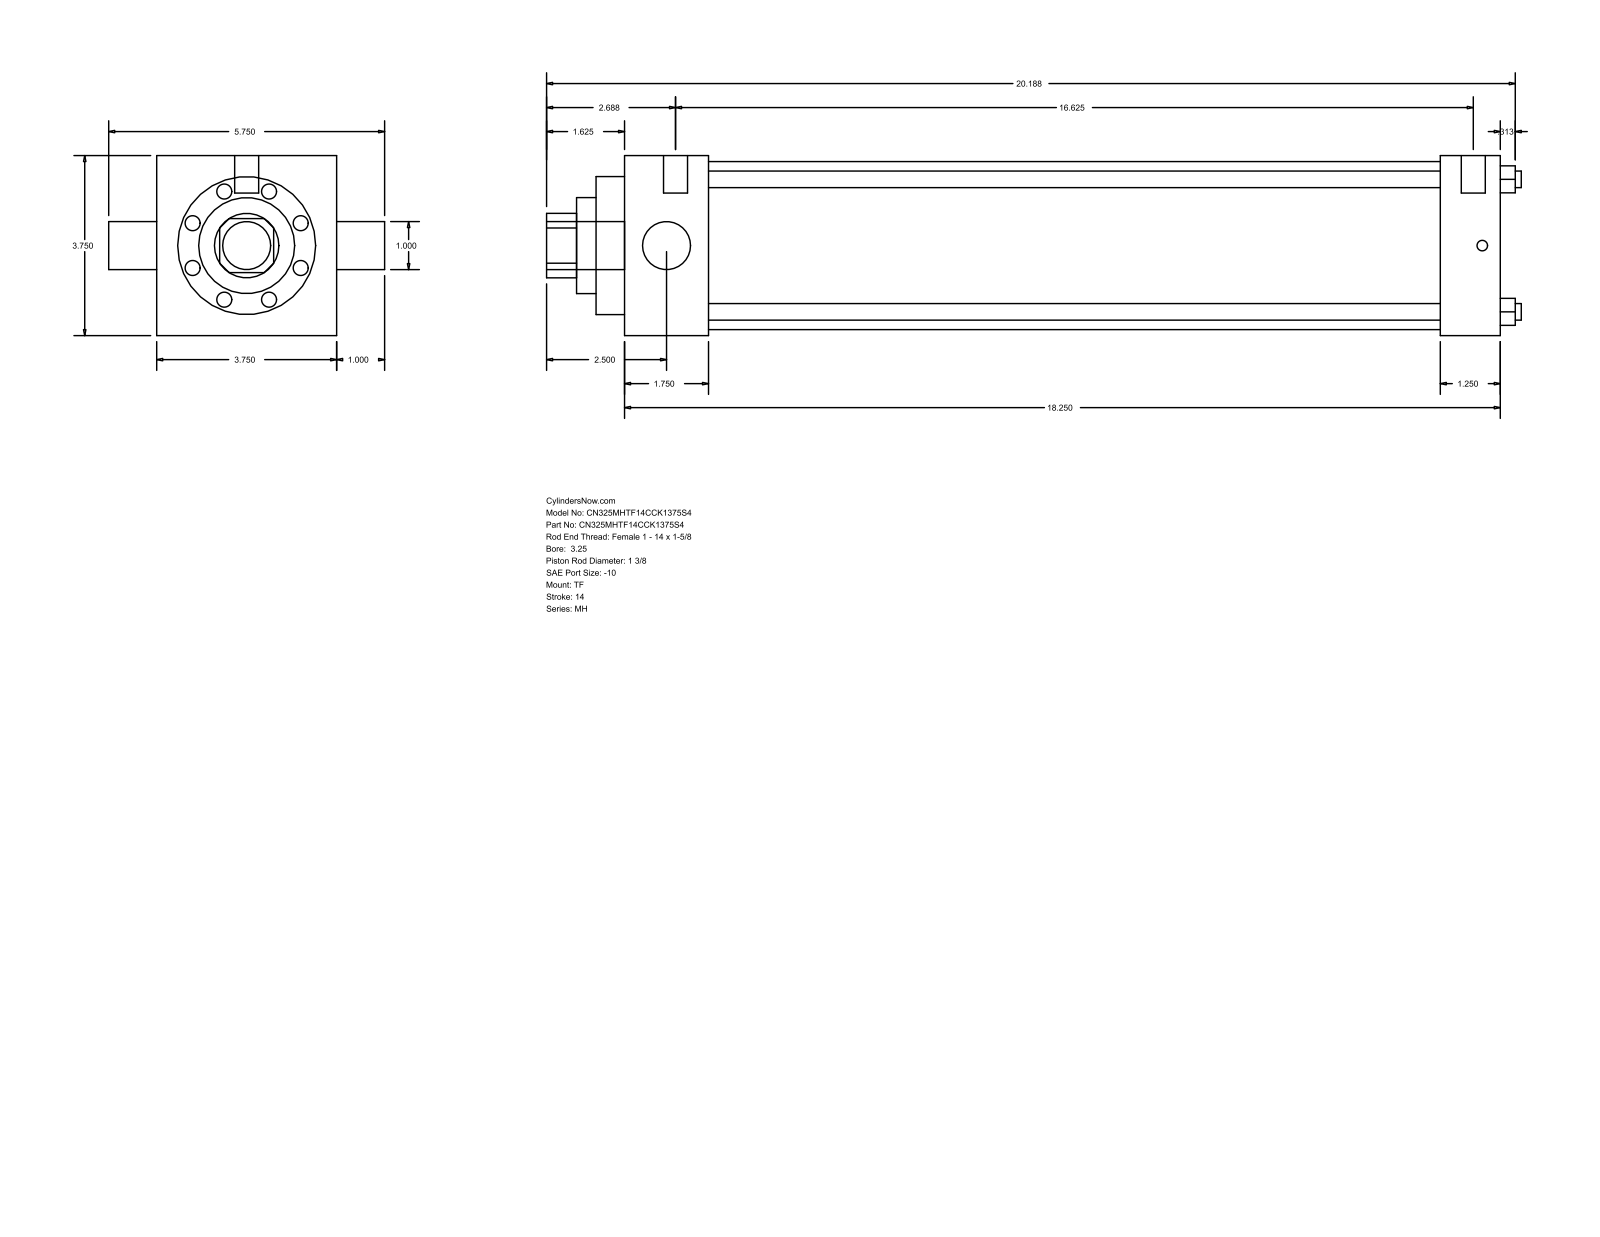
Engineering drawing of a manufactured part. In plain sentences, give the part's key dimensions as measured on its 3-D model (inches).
The part is named "MH_TF__0325_1.375". Its 3-D file was written by "GSSL Pune (CONFIG_CONTROL_DESIGN)". It is 0 solids with 86 faces: 61 planar, 25 cylindrical and 0 other. Overall it measures 20.313 by 5.75 by 3.75 inches. Round holes: 4 of diameter 0.345, 1 of diameter 1, 1 of diameter 1.375, 1 of diameter 2, 1 of diameter 2.875, 1 of diameter 3.5. Round bosses or shafts: 3 of diameter 0.219, 2 of diameter 0.5, 1 of diameter 1. Partial cylindrical surfaces (rounded edges, fillets, slot ends): 1 of radius 0.672. The main face-to-face distances are 3.75, 18.25, 1.75, 17, 15.25, 16.5, 1.25, 0.594, 2.344, 17.594. The hole center spacings are 1.952, 2.76, 3.903.
